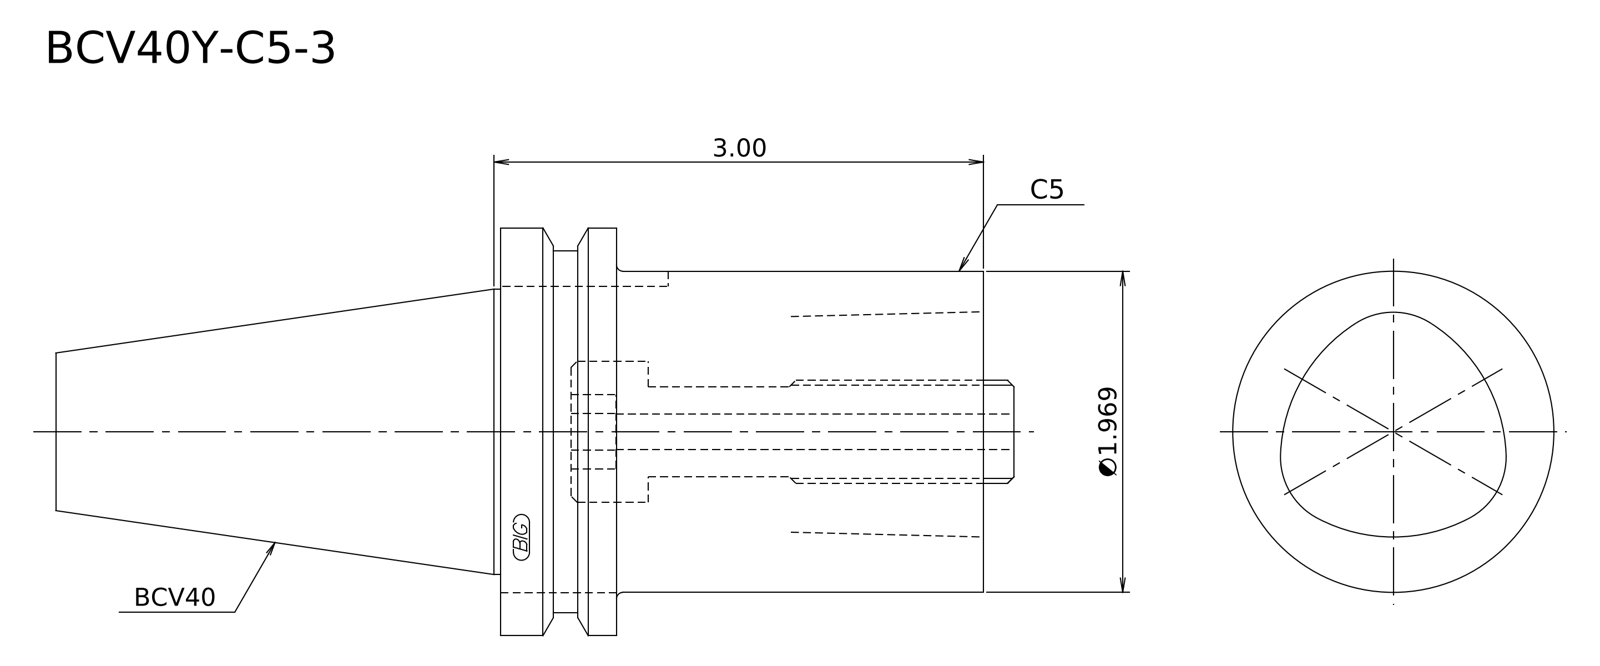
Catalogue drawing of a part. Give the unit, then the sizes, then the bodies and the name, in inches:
Units: inches
Overall size (bounding box): 5.687 × 2.5 × 2.5
Round bosses / shafts (diameter × count): ⌀2.5 ×1, ⌀2.219 ×1, ⌀1.969 ×1, ⌀1.75 ×1
Main face-to-face distances: 2.961, 2.25, 0.711, 5.687, 3.437, 2.726, 2.638, 0.388, 0.323, 3.049
Volume: 14.23 in³ · Surface area: 40.51 in²
Bodies: 1 solid, 15 faces (6 planar, 5 cylindrical, 4 other)
STEP written by: Kubotek KeyCreator 2011 V10.0.2 (22737) (automotive_design)
